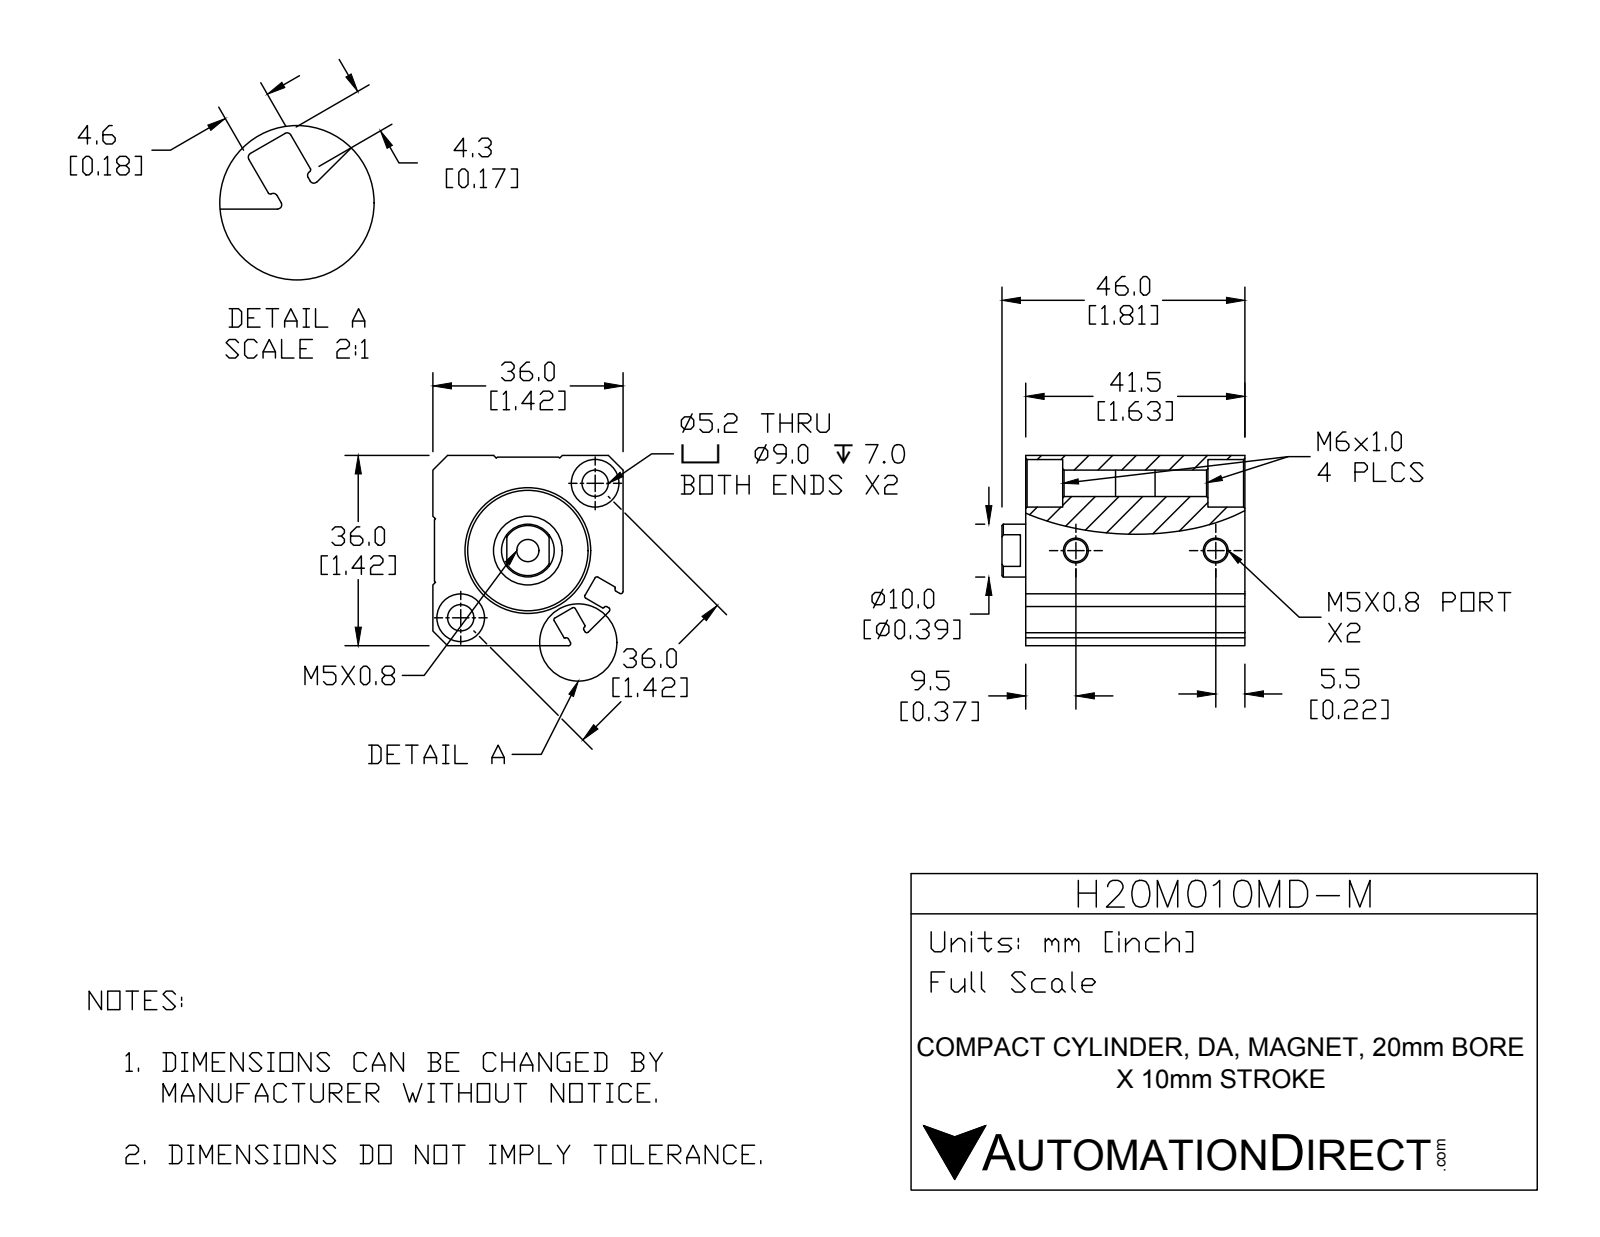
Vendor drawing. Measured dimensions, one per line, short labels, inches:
name: H20M010MD-M-BODY; H20M010MD-M-PISTON; H20M010MD-M
written by: SolidWorks 2015 (CONFIG_CONTROL_DESIGN)
unit: in
bodies: 2 solids, 141 faces (53 planar, 55 cylindrical, 33 other)
size: 1.811 × 1.417 × 1.417
volume: 2.604 in³; area: 25.07 in²
holes: 3× ⌀0.165, 2× ⌀0.197, 2× ⌀0.354, 1× ⌀0.394, 1× ⌀0.512, 1× ⌀0.787, 1× ⌀0.898
bosses: 1× ⌀0.433
rounds: 12× R0.016, 4× R0.008
face distances: 1.417, 1.406, 0.157, 1.634, 1.476, 0.102, 1.579, 0.055, 1.201, 0.181
hole spacings: 0.709, 1.043, 1.418
